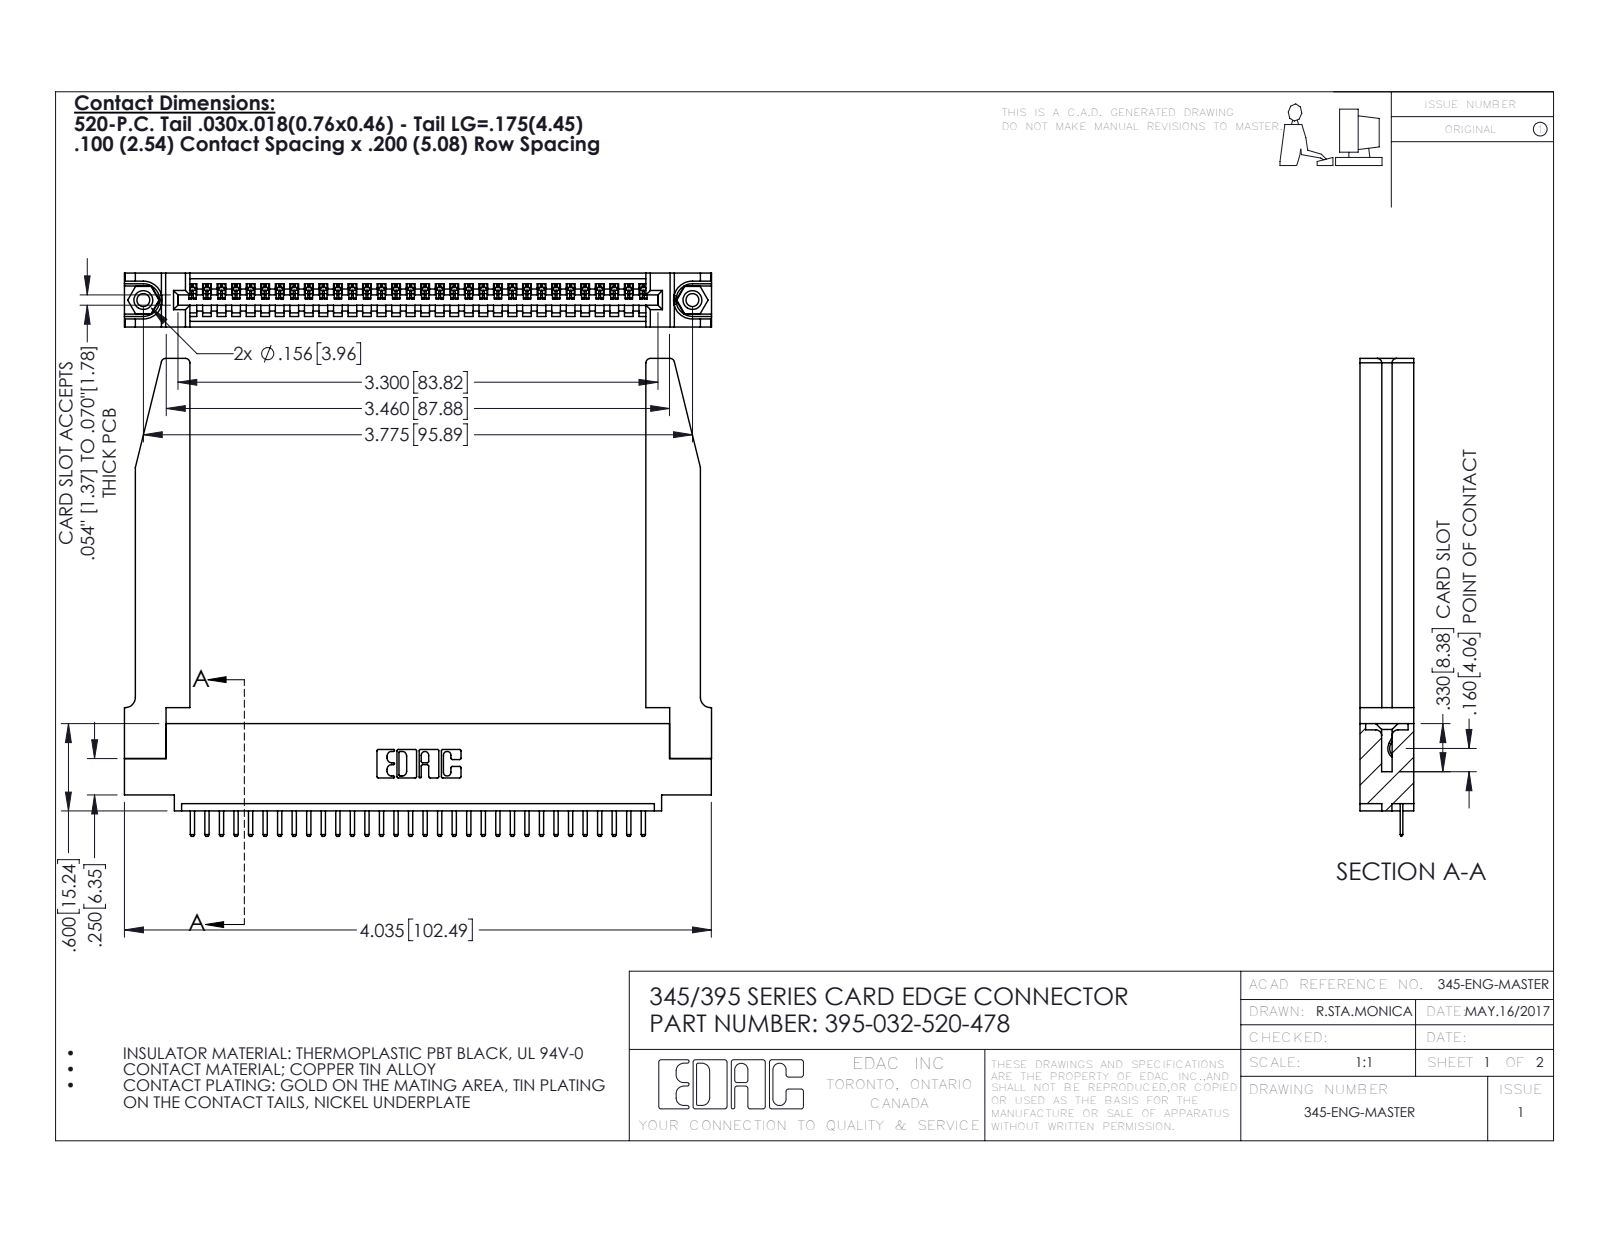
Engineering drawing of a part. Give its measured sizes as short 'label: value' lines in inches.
name: 345-292-001_345-293-120; 345-250-001_345-250-001-102; 395-032-520-478; 345 Part_0.110 Offset - 0.156 Dia-TH (+1 more)
written by: SolidWorks 2016 (CONFIG_CONTROL_DESIGN)
unit: in
bodies: 37 solids, 2348 faces (1570 planar, 726 cylindrical, 52 other)
size: 4.036 × 3.285 × 0.37
volume: 1.053 in³; area: 29.61 in²
holes: 2× ⌀0.089, 2× ⌀0.125, 2× ⌀0.156, 1× ⌀0.064
bosses: 2× ⌀0.155
rounds: 66× R0.01, 64× R0.006, 22× R0.01, 8× R0.03, 6× R0.007, 6× R0.031, 3× R0.026, 2× R0.031
face distances: 0.37, 0.072, 0.298, 0.2, 0.098, 0.272, 0.025, 0.148, 0.15, 0.225
hole spacings: 0.27, 3.54, 3.775
